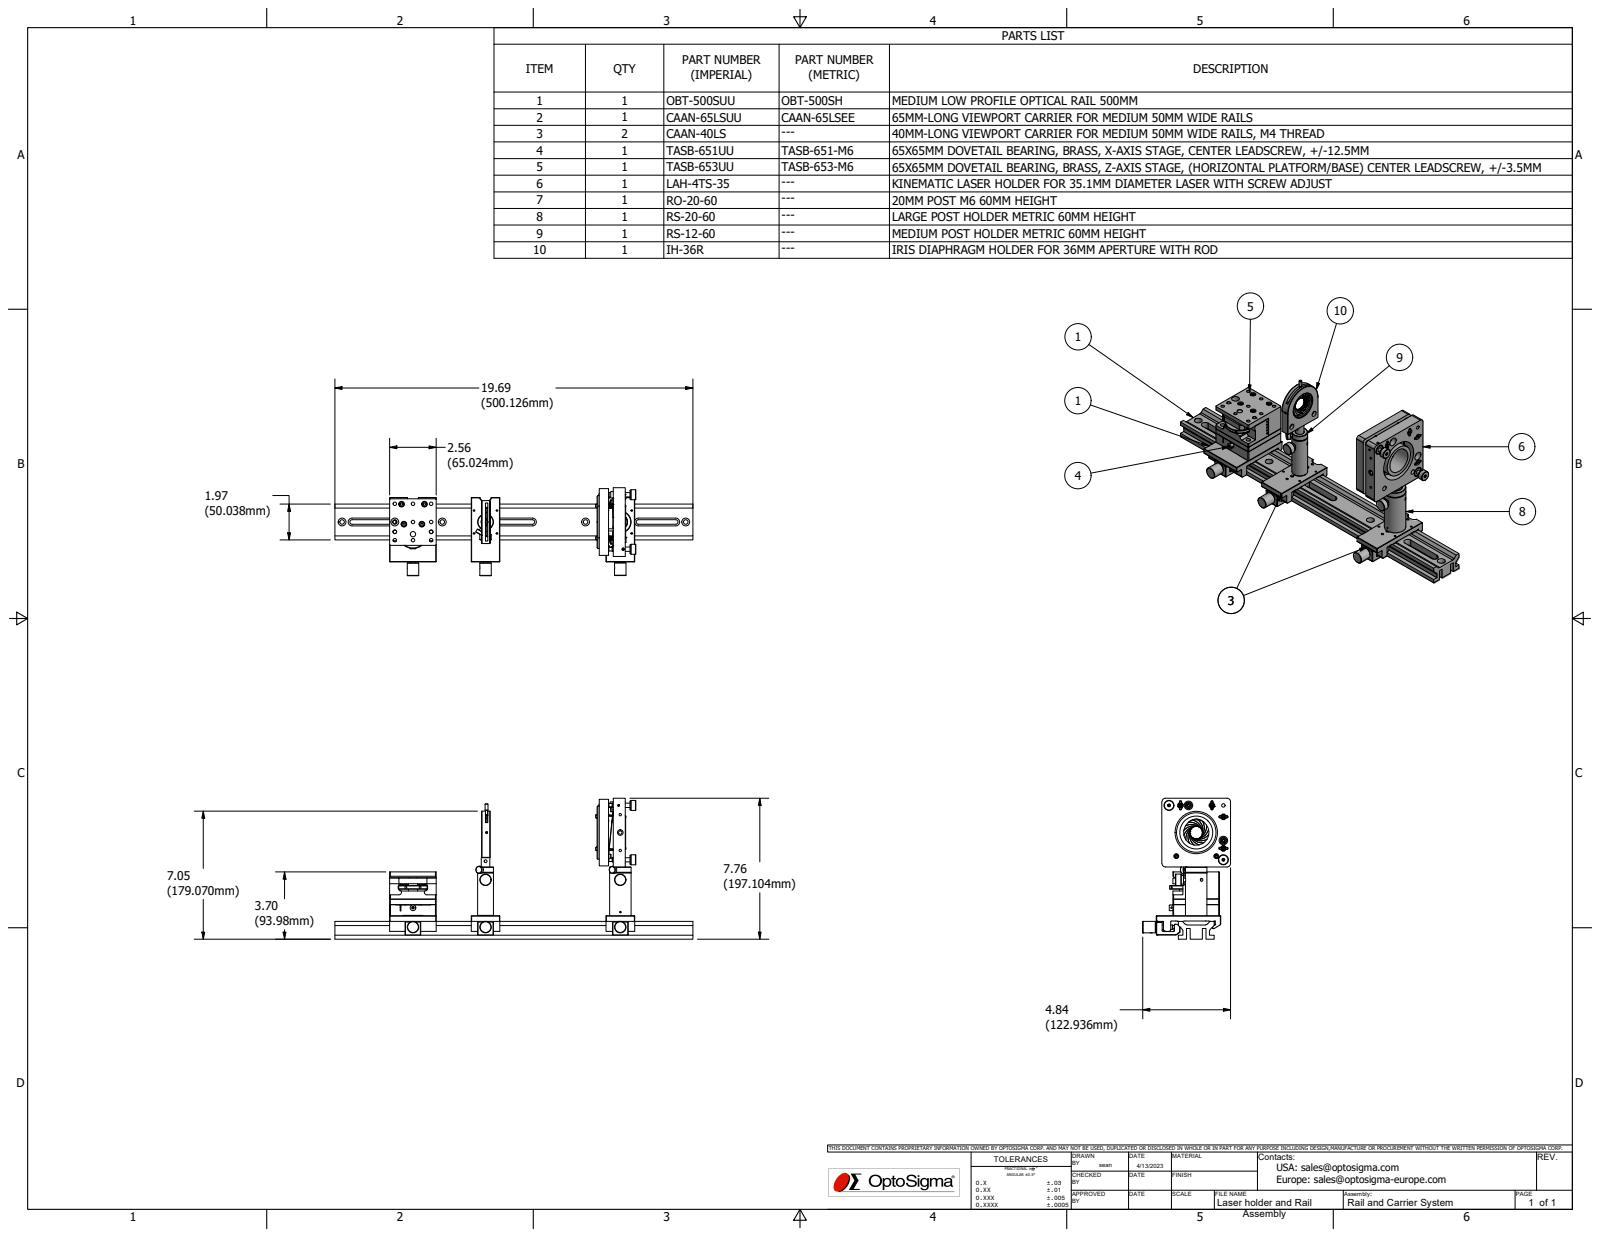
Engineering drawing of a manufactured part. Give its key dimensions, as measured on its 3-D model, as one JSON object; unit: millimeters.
{"part_name": "Rail Assembly; OBT-500SH; CAAN-65LSUU_STP; TASB-651UU (+7 more)", "step_written_by": "Autodesk Inventor 2022 (AUTOMOTIVE_DESIGN)", "units": "millimeters", "bodies": {"solids": 60, "faces": 2471, "planar": 1352, "cylindrical": 635, "other": 484}, "overall_size": [500, 197, 122.93], "volume_mm3": 1044000, "surface_area_mm2": 380877, "round_holes": [[8, 24], [2.46, 23], [4.5, 17], [1.15, 16], [2.5, 15], [5.1, 12], [4.98, 9], [5, 9], [11, 9], [3.3, 8], [6.5, 7], [3, 6]], "round_bosses_or_shafts": [[0.8, 24], [1.1, 16], [4, 11], [3, 11], [2.2, 10], [16, 7], [6, 7], [5.5, 6]], "partial_cylinders_radius": [[1, 18], [1.5, 18], [1.4, 16], [3, 14], [4, 8], [6, 8], [5, 7], [3.25, 6]], "face_to_face_distances": [5, 13, 33.5, 8, 5.1, 22.1, 17, 19.9, 20, 33], "hole_center_spacings": [25.4, 56.8, 289.76, 35.92, 50.8, 10, 16, 22.63]}
